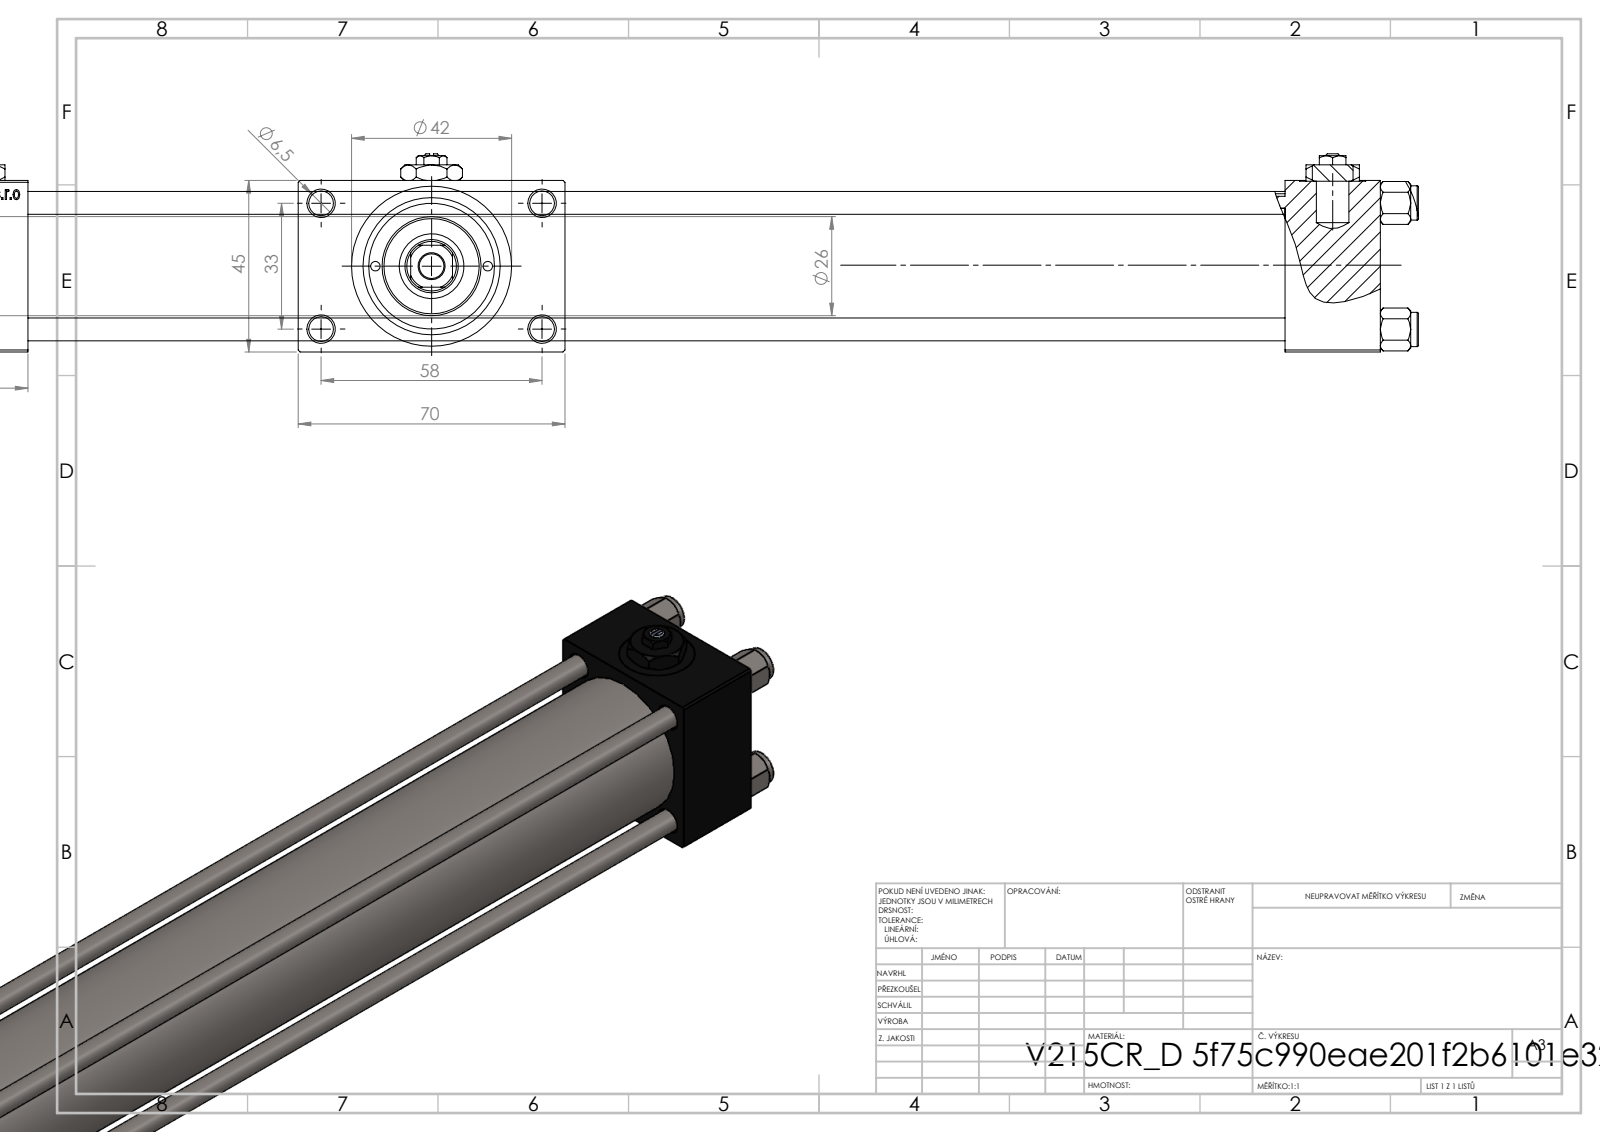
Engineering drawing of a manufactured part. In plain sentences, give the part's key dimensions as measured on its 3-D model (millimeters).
The part is named "V215CR_D_TYCINKA; Zatka_pro_OIL_PORT; V215CR_D_Body; V215CR_VCP_D (+2 more)". Its 3-D file was written by "SolidWorks 2019 (CONFIG_CONTROL_DESIGN)". It is 13 solids with 1209 faces: 544 planar, 103 cylindrical and 562 other. Overall it measures 438 by 70 by 52 millimeters. Its volume is 396 039 cubic millimeters and its surface area 172 121 square millimeters. Round holes: 5 of diameter 6.5, 4 of diameter 6, 4 of diameter 13.16, 4 of diameter 20, 3 of diameter 7, 2 of diameter 2.5, 1 of diameter 14, 1 of diameter 17, 1 of diameter 24, 1 of diameter 32, 1 of diameter 33. Round bosses or shafts: 4 of diameter 9, 1 of diameter 42, 1 of diameter 38, 1 of diameter 26. Partial cylindrical surfaces (rounded edges, fillets, slot ends): 1 of radius 6.5. The main face-to-face distances are 45, 25, 12.5, 330, 355, 57.5, 368, 38, 393, 70. The hole center spacings are 12.4, 16.7, 21.8, 23.48, 33.2, 33.37, 35.35, 35.47.
